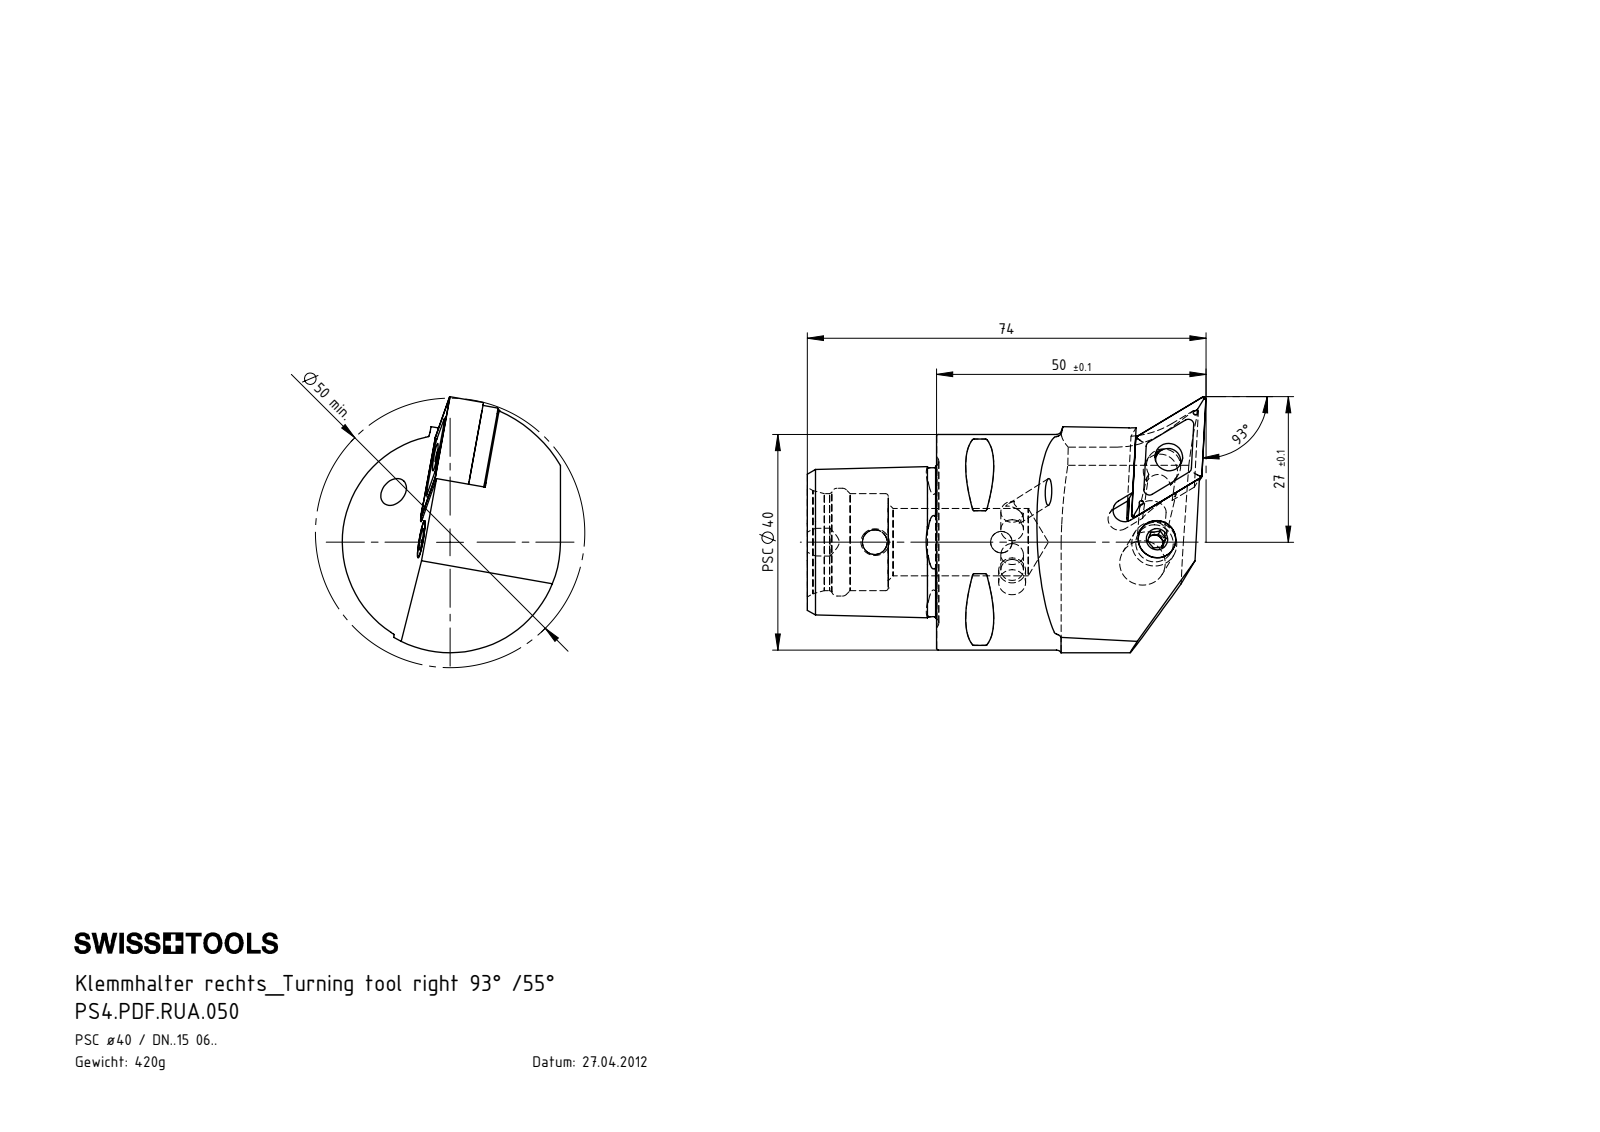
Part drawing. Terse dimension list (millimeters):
name: PS4-PDF.RUA.050; WDF-ER2.101.003_A; WCD-ER4.101.017_A; WCD-ER1.101.000 (+4 more)
written by: SolidWorks 2012 (CONFIG_CONTROL_DESIGN)
unit: mm
bodies: 8 solids, 346 faces (91 planar, 83 cylindrical, 172 other)
size: 74 × 47.5 × 40.5
volume: 54 509 mm³; area: 16 311 mm²
holes: 2× ⌀4, 2× ⌀4.2, 1× ⌀4.6, 1× ⌀5, 1× ⌀5.16, 1× ⌀6.4, 1× ⌀7, 1× ⌀8.4, 1× ⌀12.5, 1× ⌀18, 1× ⌀20
bosses: 1× ⌀40, 1× ⌀8, 1× ⌀7.9, 1× ⌀6.4, 1× ⌀5, 1× ⌀4.7, 1× ⌀3.55
rounds: 8× R0.3, 4× R0.4, 4× R1, 2× R2.5, 1× R0.8, 1× R2.1, 1× R2.35, 1× R2.8
face distances: 6.02, 3.18, 9.2, 12.7, 12.3, 24, 4.85, 0.4, 15.52, 5.6
hole spacings: 15.59, 23.5
